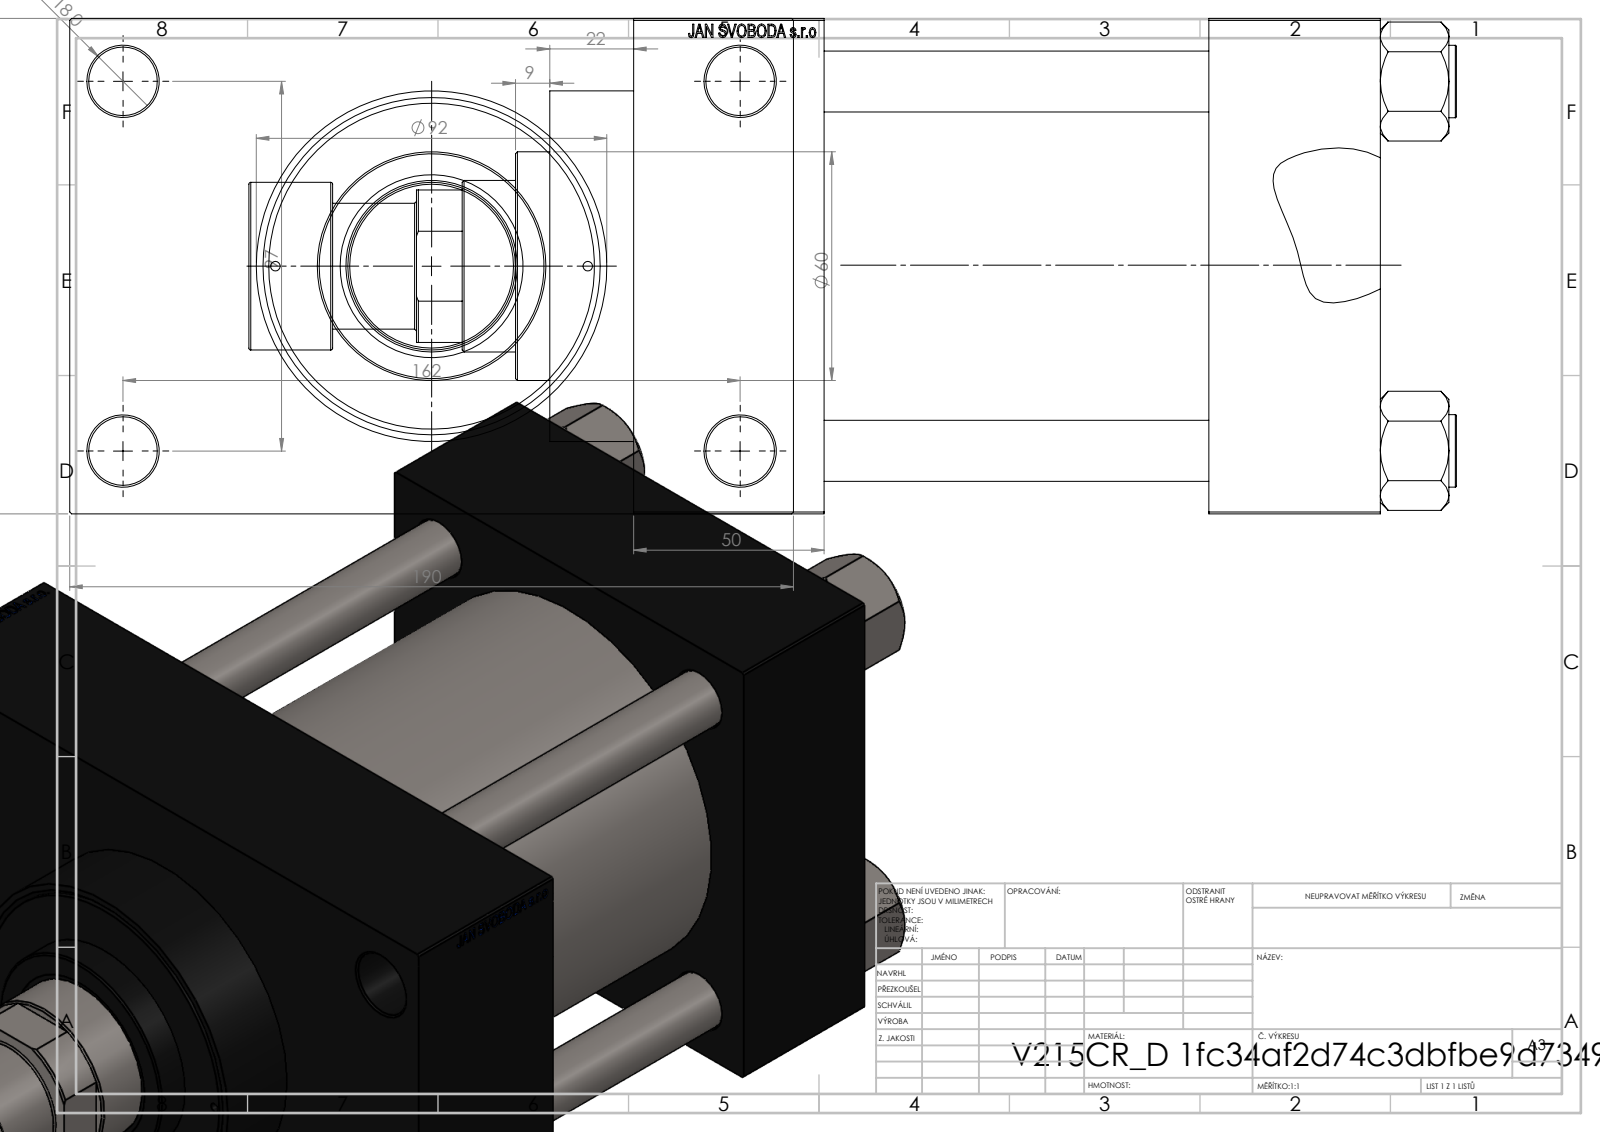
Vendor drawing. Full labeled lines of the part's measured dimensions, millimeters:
Part name (STEP PRODUCT): V215CR_D_TYCINKA; V215_VC_A; V215CR_VCP_D; NUT_M5_D (+2 more)
STEP written by: SolidWorks 2019 (CONFIG_CONTROL_DESIGN)
Units: millimetres
Bodies: 12 solids, 1172 faces (550 planar, 96 cylindrical, 526 other)
Overall size (bounding box): 317 × 190 × 130
Volume: 2 743 000 mm³ · Surface area: 392 789 mm²
Round holes (diameter × count): ⌀16 ×4, ⌀18 ×4, ⌀2.5 ×2, ⌀7 ×2, ⌀26.44 ×2, ⌀35 ×2, ⌀31.5 ×1, ⌀45 ×1, ⌀48 ×1, ⌀76 ×1, ⌀85.5 ×1, ⌀100 ×1
Round bosses / shafts (diameter × count): ⌀19 ×4, ⌀106 ×1, ⌀92 ×1, ⌀60 ×1, ⌀44 ×1, ⌀33 ×1
Main face-to-face distances: 50, 130, 101, 151, 45, 146, 196, 30, 160, 96
Hole centre spacings: 32.55, 49.02, 62.87, 68.52, 94.41, 96.9, 101.73, 102.27
